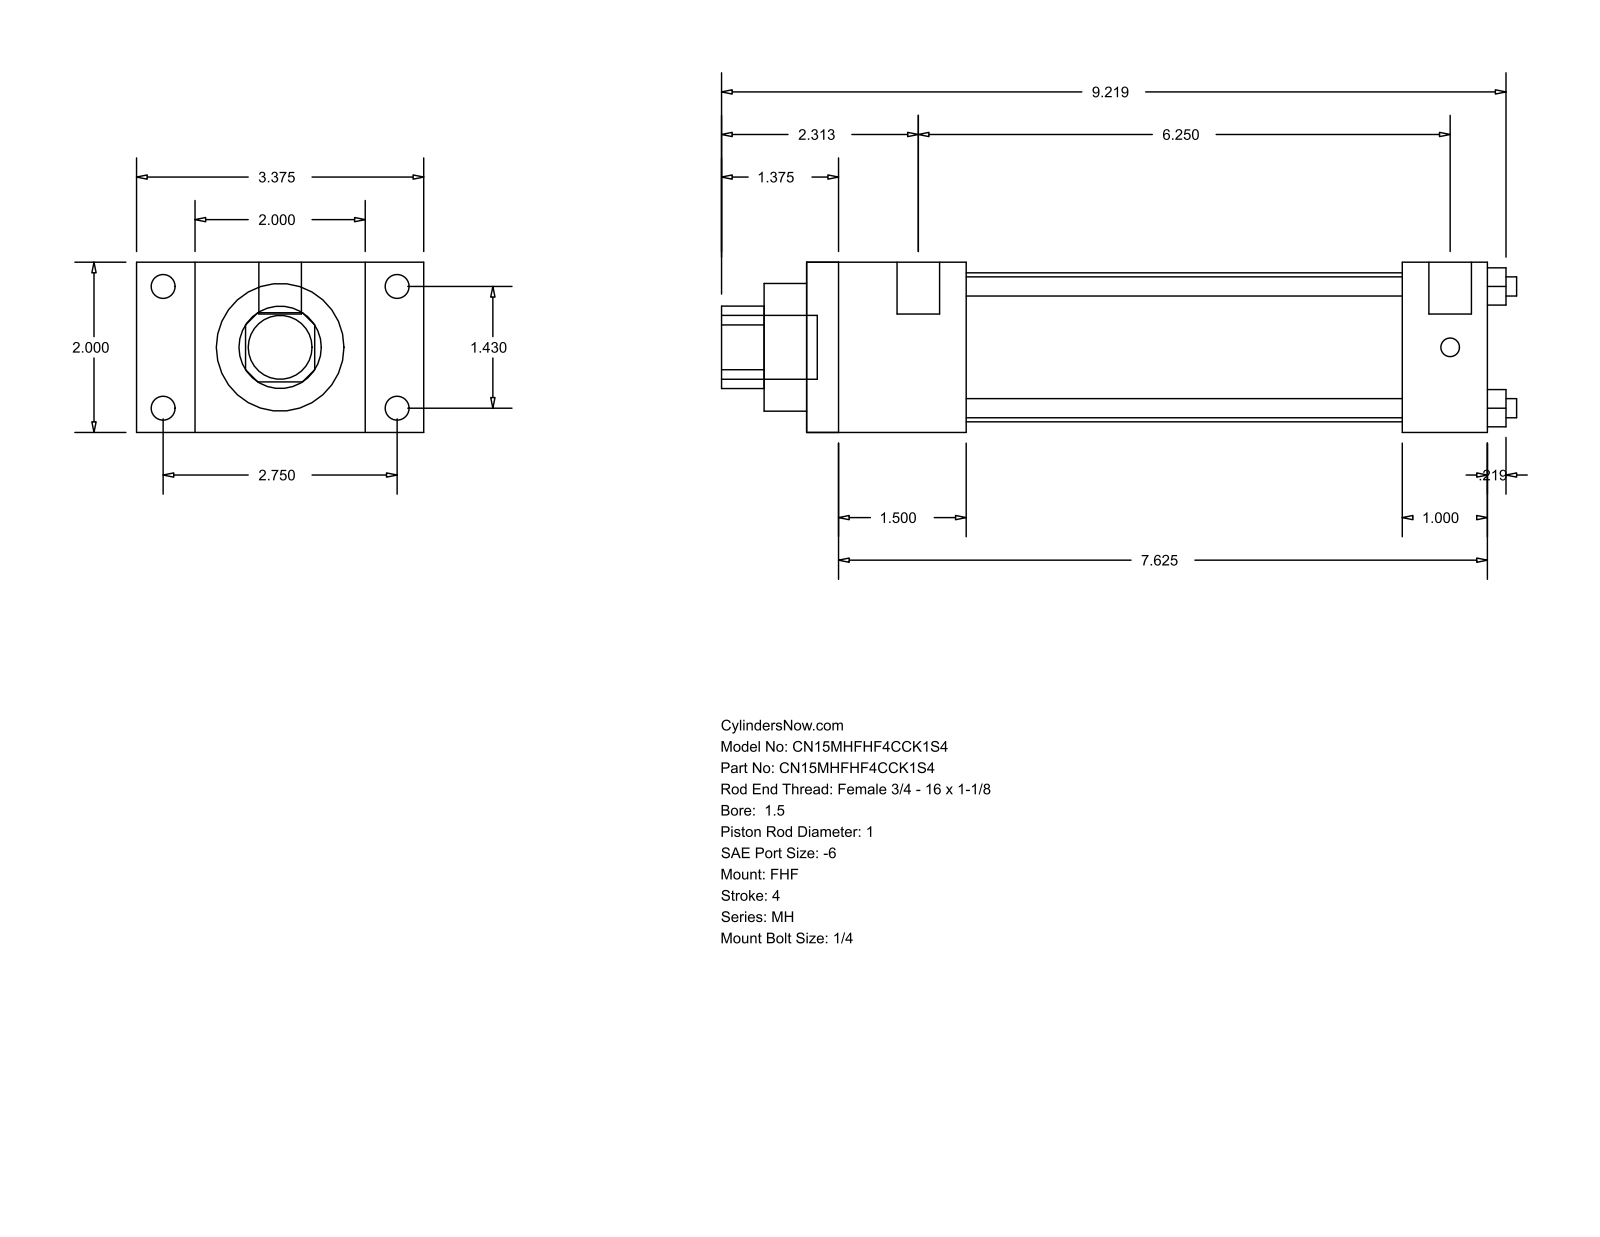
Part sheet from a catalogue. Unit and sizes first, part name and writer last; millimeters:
Units: millimetres
Overall size (bounding box): 237.33 × 85.72 × 50.8
Round holes (diameter × count): ⌀5.71 ×4, ⌀25.4 ×1, ⌀38.1 ×1, ⌀44.45 ×1
Round bosses / shafts (diameter × count): ⌀7.14 ×4, ⌀5.56 ×4, ⌀12.7 ×2, ⌀19.05 ×1
Partial cylindrical surfaces — rounded edges, fillets, slot ends (radius × count): R12.29 ×1
Main face-to-face distances: 50.8, 17.46, 68.26, 47.63, 85.72, 203.2, 155.57, 25.4, 177.8, 130.17
Hole centre spacings: 25.68, 36.32, 51.36
Bodies: 0 solids, 88 faces (60 planar, 28 cylindrical, 0 other)
Part name (STEP PRODUCT): MH_FHF__0150_1
STEP written by: GSSL Pune (CONFIG_CONTROL_DESIGN)
